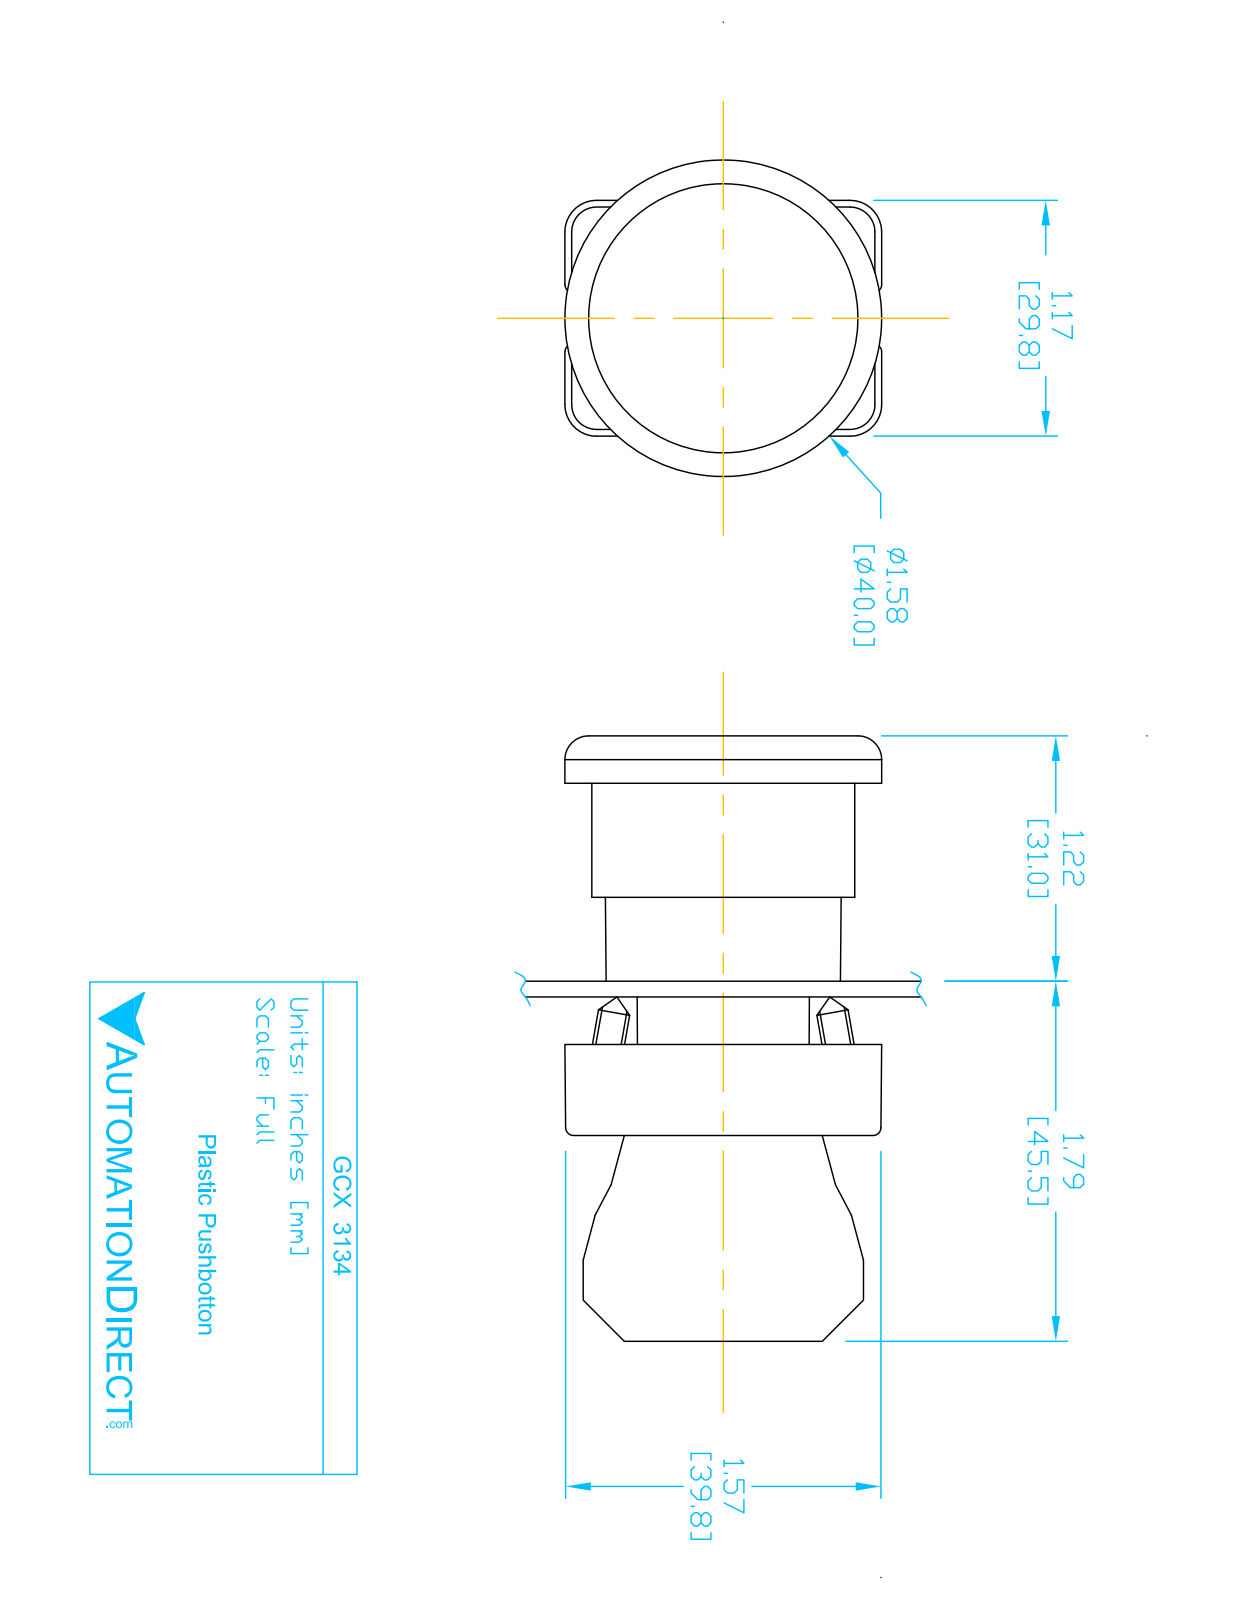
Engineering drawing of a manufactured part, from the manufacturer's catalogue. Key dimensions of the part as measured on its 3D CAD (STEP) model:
Part name (STEP PRODUCT): ECX3029-2; ecx1040; GCX3134; GCX3134 OPERATOR
STEP written by: SolidWorks 2016 (AUTOMOTIVE_DESIGN)
Units: inches
Bodies: 6 solids, 389 faces (224 planar, 134 cylindrical, 31 other)
Overall size (bounding box): 2.944 × 1.581 × 1.575
Volume: 1.827 in³ · Surface area: 33.4 in²
Round holes (diameter × count): ⌀0.079 ×2, ⌀0.124 ×2, ⌀0.13 ×2, ⌀0.087 ×1, ⌀0.197 ×1, ⌀0.878 ×1, ⌀0.888 ×1, ⌀1.024 ×1, ⌀1.181 ×1
Round bosses / shafts (diameter × count): ⌀0.157 ×2, ⌀1.299 ×1, ⌀1.175 ×1, ⌀0.945 ×1, ⌀0.856 ×1, ⌀0.78 ×1
Partial cylindrical surfaces — rounded edges, fillets, slot ends (radius × count): R0.059 ×24, R0.041 ×12, R0.124 ×12, R0.157 ×12, R0.039 ×4, R0.128 ×2, R0.02 ×1, R0.063 ×1
Main face-to-face distances: 1.921, 0.579, 0.033, 1.763, 0.157, 0.031, 0.72, 1.043, 1.2, 0.689
Hole centre spacings: 0.236, 0.544, 0.472, 0.49
